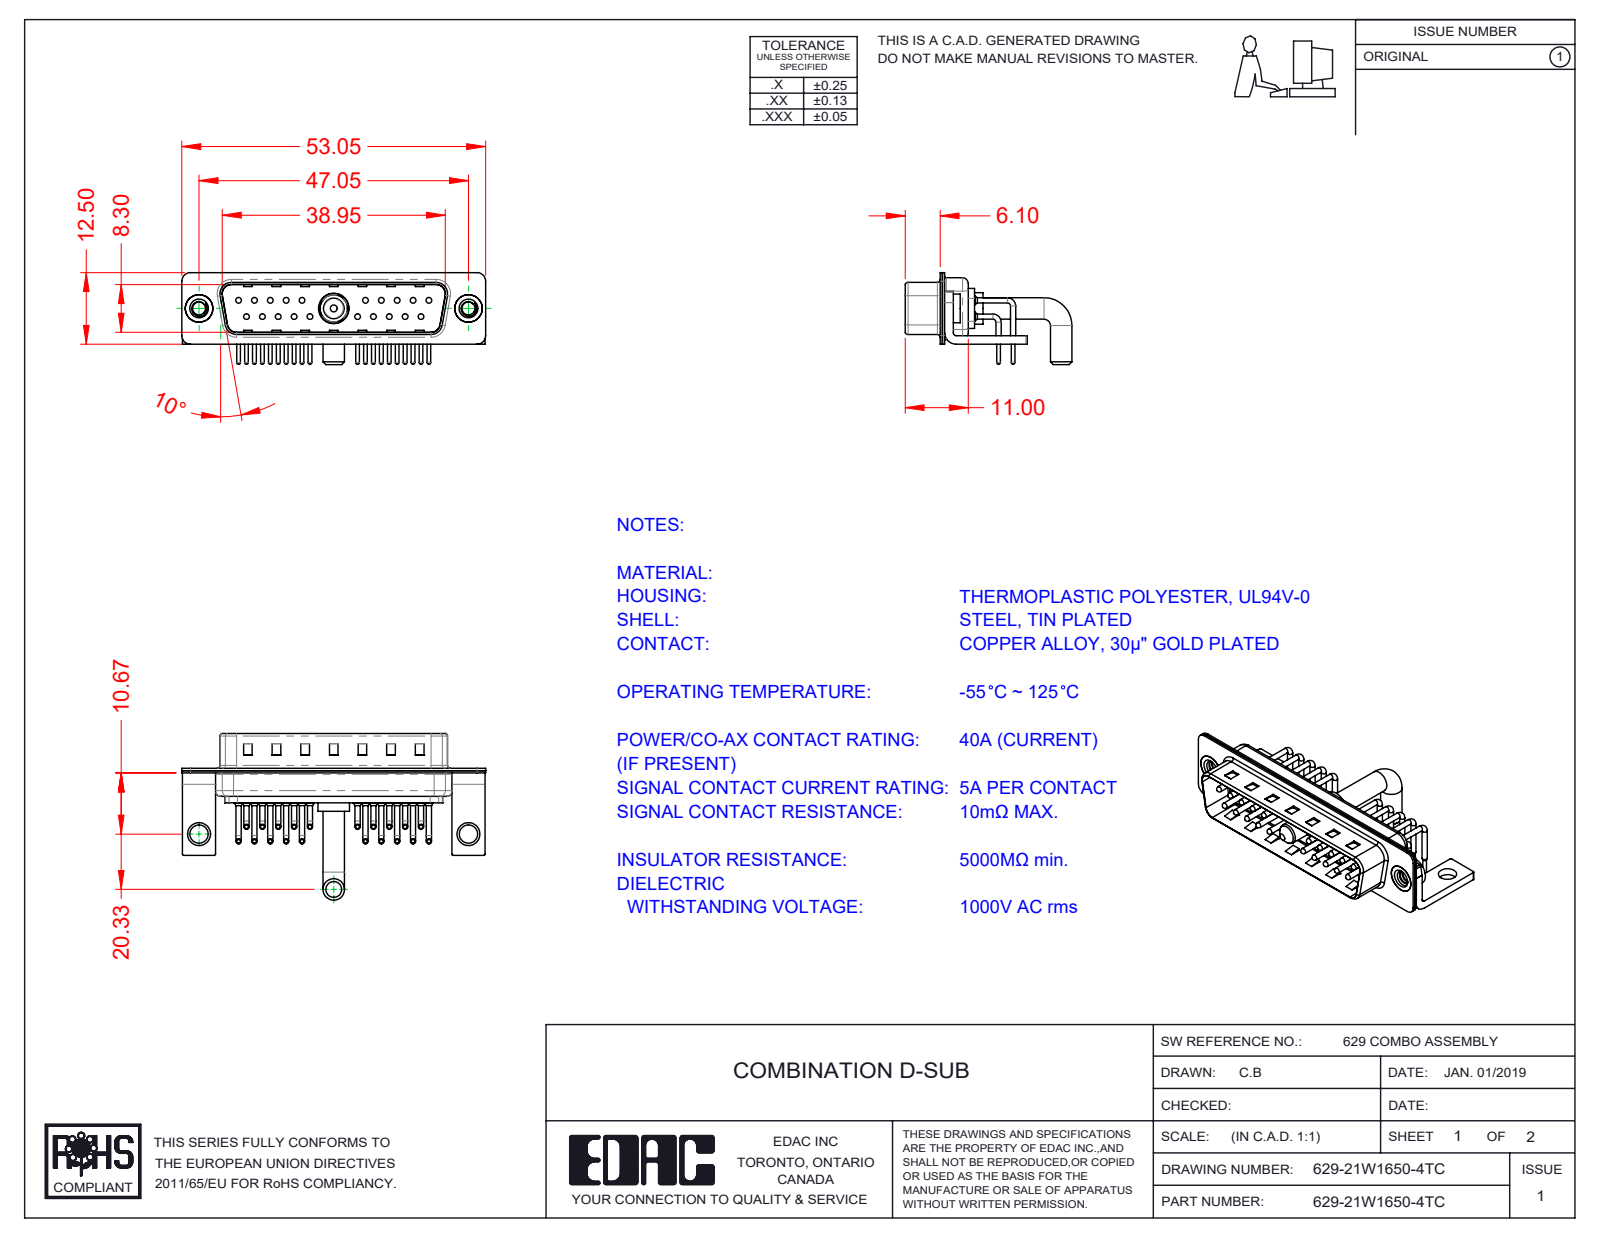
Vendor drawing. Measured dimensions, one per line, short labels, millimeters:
name: 629Combo Shell Front_25 Contacts; Power Pin_Ext 40A RA; 629Combo Shell Rear_25 Contacts; 629Combo Threaded Rivet_2 (+5 more)
written by: SolidWorks 2020 (CONFIG_CONTROL_DESIGN)
unit: mm
bodies: 29 solids, 2667 faces (1481 planar, 902 cylindrical, 284 other)
size: 53.05 × 29.11 × 16.05
volume: 3 481 mm³; area: 8 366 mm²
holes: 20× ⌀0.75, 20× ⌀1.6, 20× ⌀2, 2× ⌀2.26, 2× ⌀3.2, 2× ⌀4, 2× ⌀4.8, 1× ⌀4.85, 1× ⌀5.3
bosses: 40× ⌀0.9, 20× ⌀1.5, 20× ⌀1, 20× ⌀0.65, 2× ⌀5, 2× ⌀4.9, 2× ⌀3.75, 1× ⌀5.5
rounds: 20× R1.01, 16× R0.25, 16× R1.5, 13× R2, 9× R0.5, 8× R1.6, 4× R0.6, 4× R0.65
face distances: 0.4, 0.8, 9.5, 1.5, 9.1, 8.7, 9.9, 0.6, 1.2, 2.1
hole spacings: 3.16, 2.77, 5.54, 8.31, 5.04, 19.39, 20.97, 22.16
